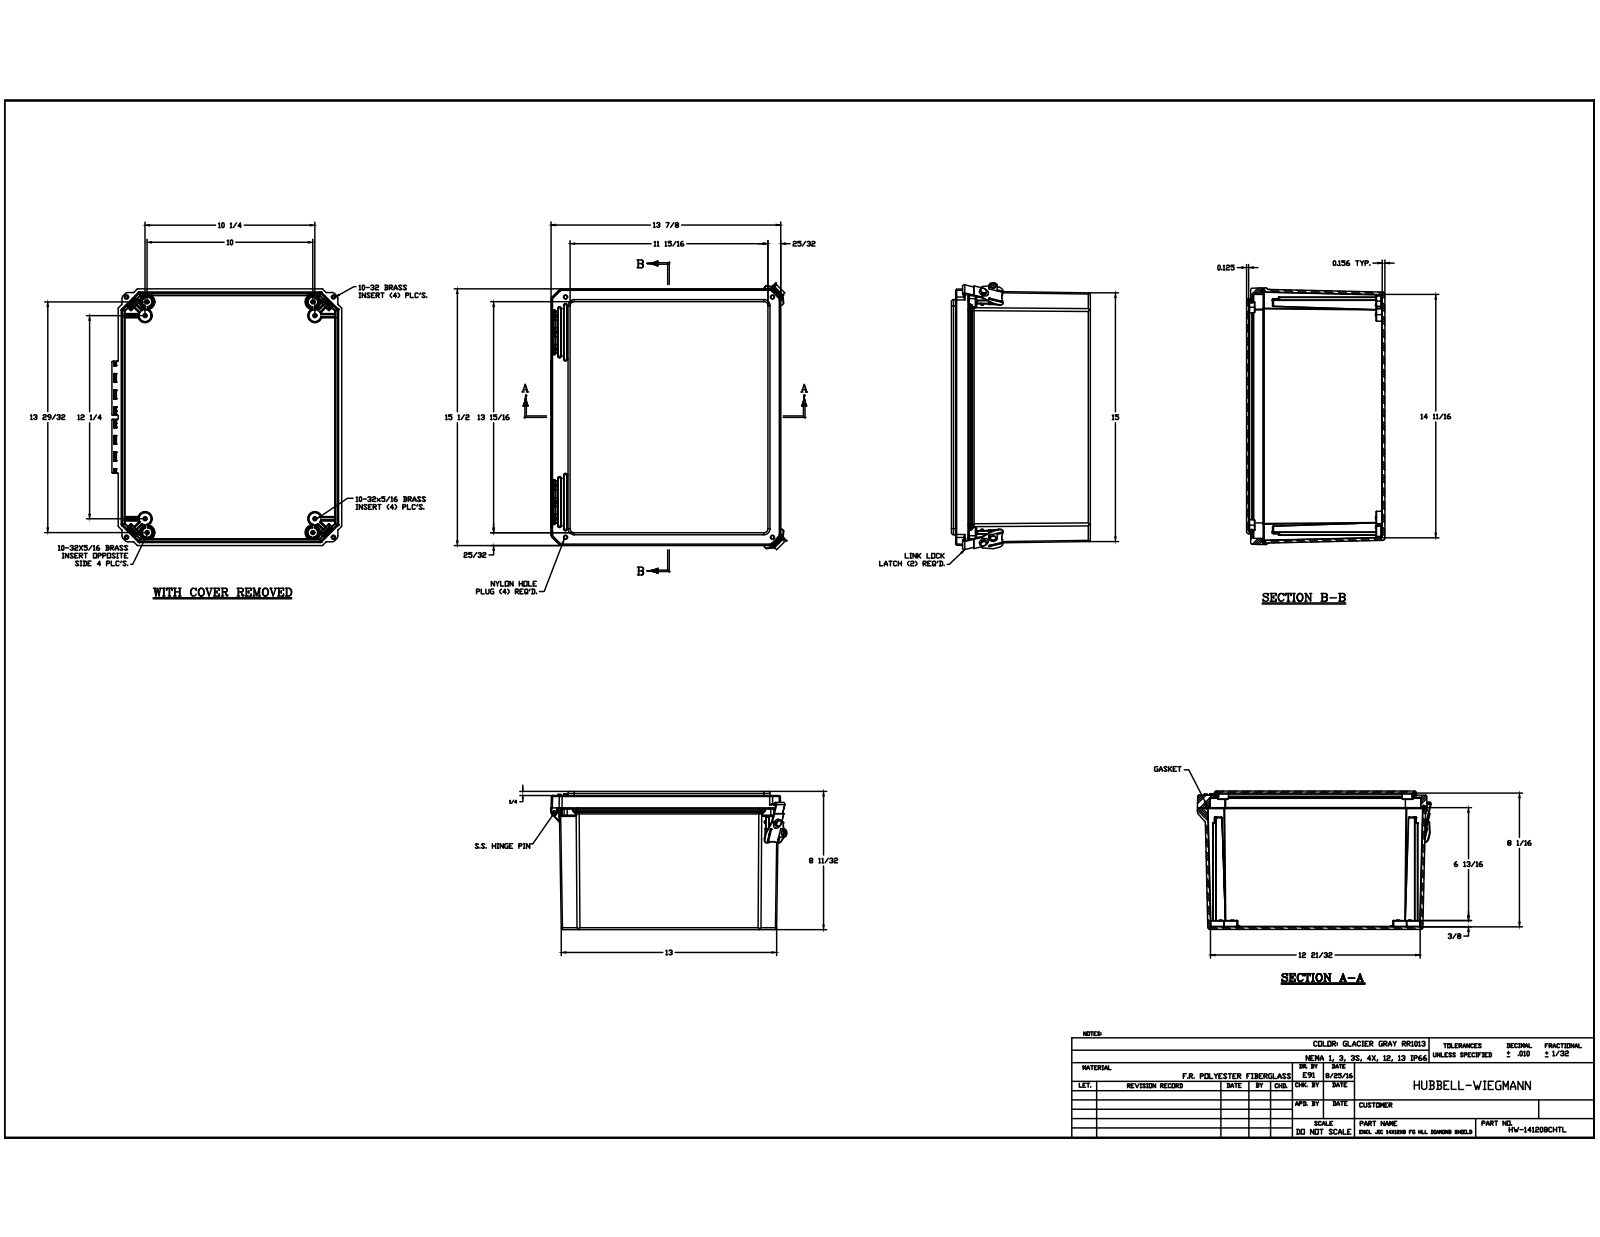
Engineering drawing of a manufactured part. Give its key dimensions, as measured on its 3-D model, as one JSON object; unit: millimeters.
{"part_name": "DS141208HLL_STP; DS141208BOX; BRASS INSERT-(; BRASS INSERT-(_1 (+7 more)", "step_written_by": "Autodesk Inventor 2017 (CONFIG_CONTROL_DESIGN)", "units": "millimeters", "bodies": {"solids": 35, "faces": 2356, "planar": 820, "cylindrical": 920, "other": 616}, "overall_size": [417.77, 364.72, 219.73], "volume_mm3": 2382000, "surface_area_mm2": 1195000, "round_holes": [[3.96, 16], [3.86, 8], [2.49, 4], [3.81, 4], [6.4, 4], [6.43, 4], [1.27, 2], [3.05, 2], [5.56, 2], [5.77, 2], [7.94, 2], [9.22, 2]], "round_bosses_or_shafts": [[6.25, 16], [5.3, 4], [5.08, 4], [3.43, 3], [1.27, 3], [15.24, 2], [11.05, 2]], "partial_cylinders_radius": [[0.25, 195], [0.13, 88], [0.51, 49], [0.76, 45], [3.17, 34], [0.99, 28], [1.59, 28], [0.76, 24]], "face_to_face_distances": [3.96, 3.17, 207.91, 211.87, 4.07, 4.03, 208.7, 204.74, 6.35, 3.18], "hole_center_spacings": [351.43, 20.15, 21.02, 32.52, 32.54, 40.22, 40.23, 258.01]}
